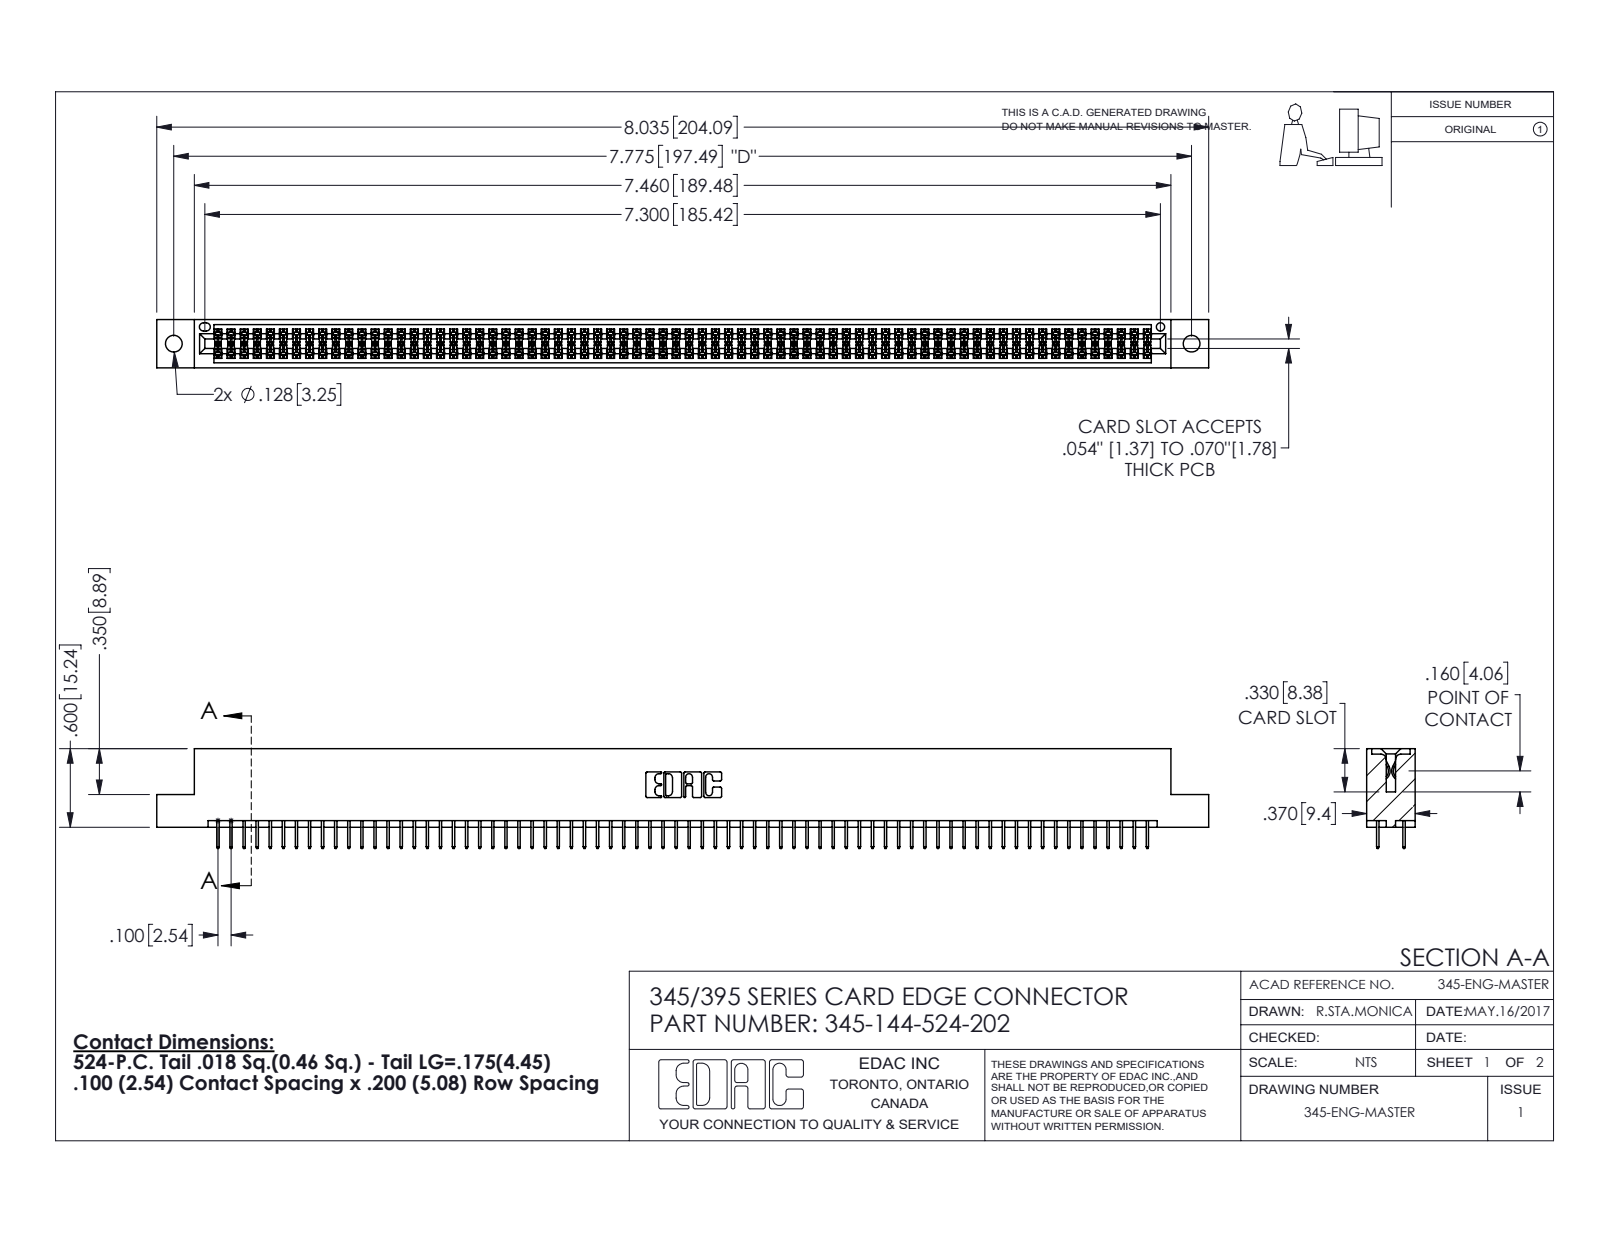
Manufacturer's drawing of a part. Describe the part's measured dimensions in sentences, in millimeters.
The part is named "345-292-001_345-293-124; 345-144-524-202; 345 Part_Flush Mounting Lugs - 0.128 Dia". Its 3-D file was written by "SolidWorks 2016 (CONFIG_CONTROL_DESIGN)". It is 145 solids with 7902 faces: 5696 planar, 2206 cylindrical and 0 other. Overall it measures 204.1 by 19.4 by 9.4 millimeters. Its volume is 19 840 cubic millimeters and its surface area 29 070 square millimeters. Round holes: 2 of diameter 3.3, 1 of diameter 1.6. Partial cylindrical surfaces (rounded edges, fillets, slot ends): 216 of radius 0.2, 22 of radius 0.3, 6 of radius 0.2, 6 of radius 0.8, 3 of radius 0.7, 2 of radius 0.4, 2 of radius 0.5, 2 of radius 0.6. The main face-to-face distances are 7.6, 1.8, 5.1, 9.4, 2.5, 6.9, 0.6, 5.7, 1.8, 4.4. The hole center spacings are 6.9, 191.5, 197.5.
